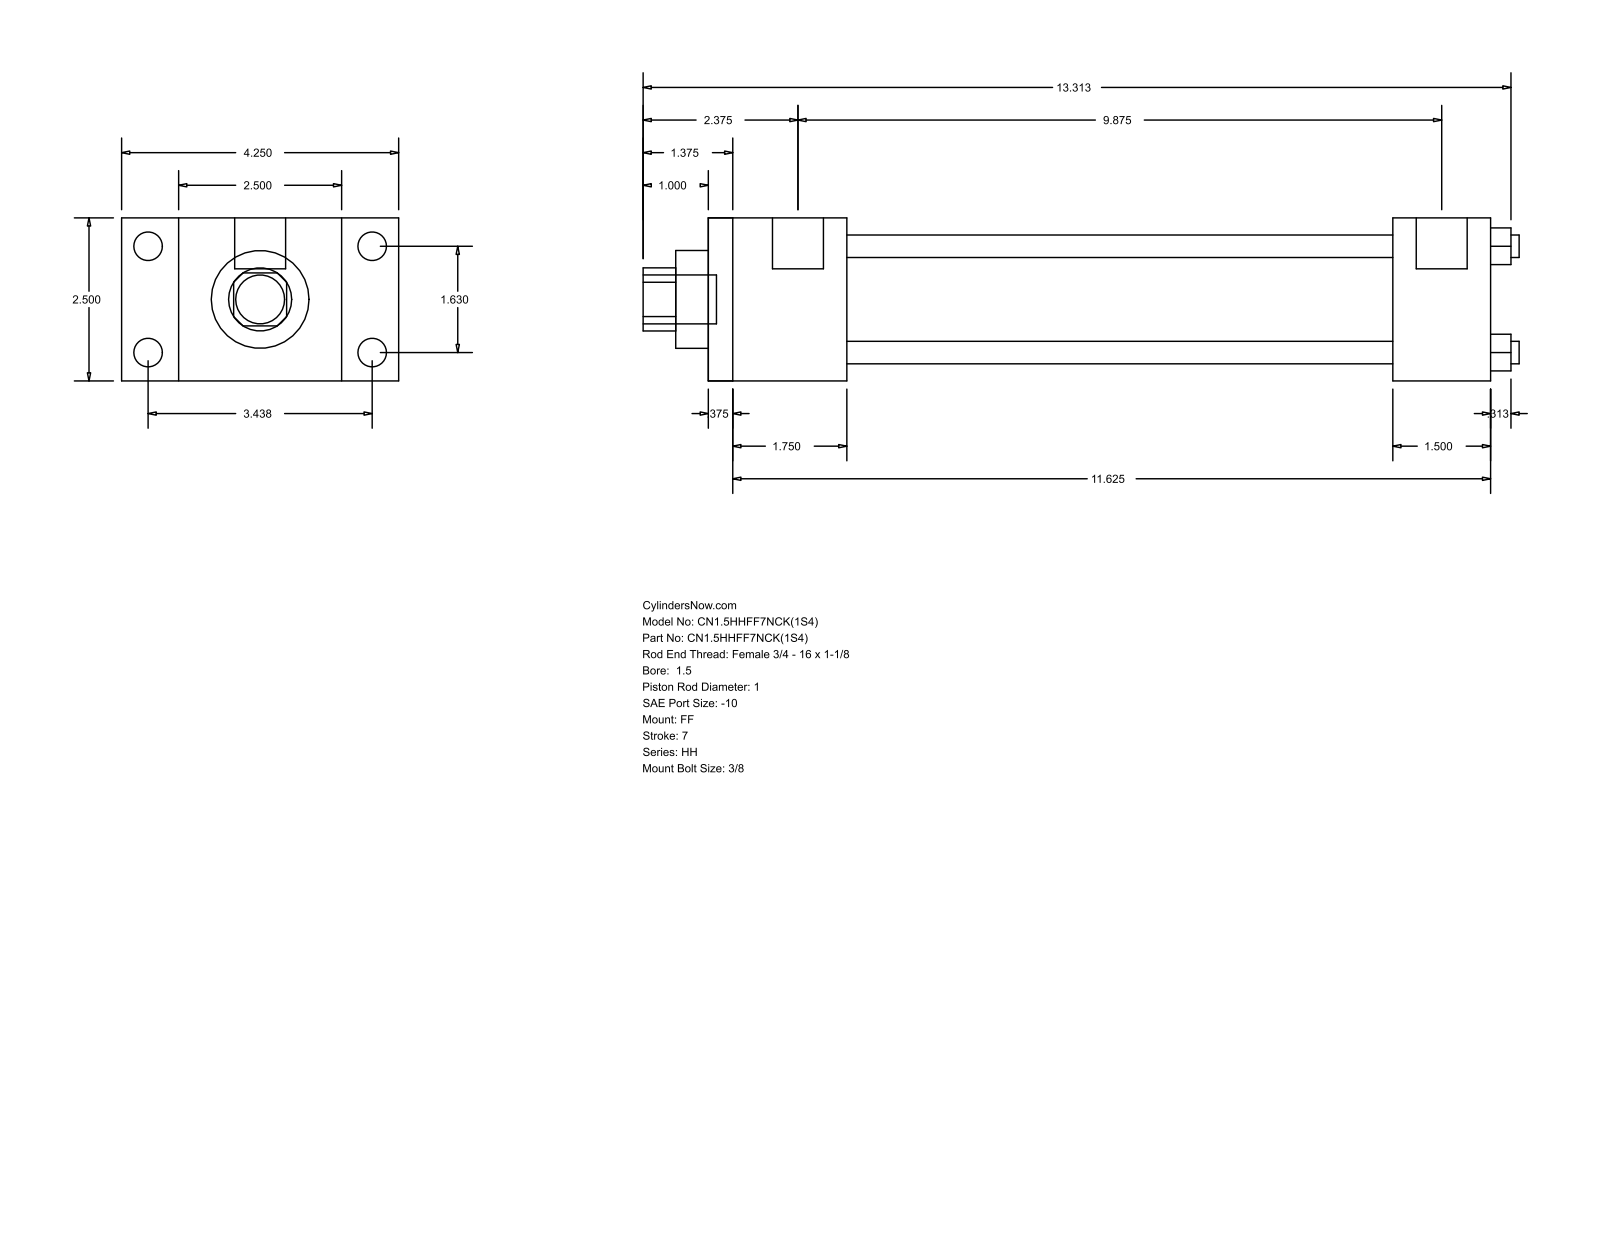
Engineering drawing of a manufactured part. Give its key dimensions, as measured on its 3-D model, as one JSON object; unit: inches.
{"part_name": "HH_FF__0150_1", "step_written_by": "GSSL Pune (CONFIG_CONTROL_DESIGN)", "units": "inches", "bodies": {"solids": 0, "faces": 92, "planar": 64, "cylindrical": 28, "other": 0}, "overall_size": [13.437, 4.25, 2.5], "round_holes": [[0.345, 4], [1, 1], [1.5, 1], [1.75, 1]], "round_bosses_or_shafts": [[0.438, 4], [0.219, 4], [0.781, 2], [0.75, 1]], "partial_cylinders_radius": [[0.484, 1]], "face_to_face_distances": [2.5, 12, 0.375, 11.625, 2.125, 1.75, 9.875, 10.5, 10.125, 8.375], "hole_center_spacings": [1.152, 1.63, 2.305]}
